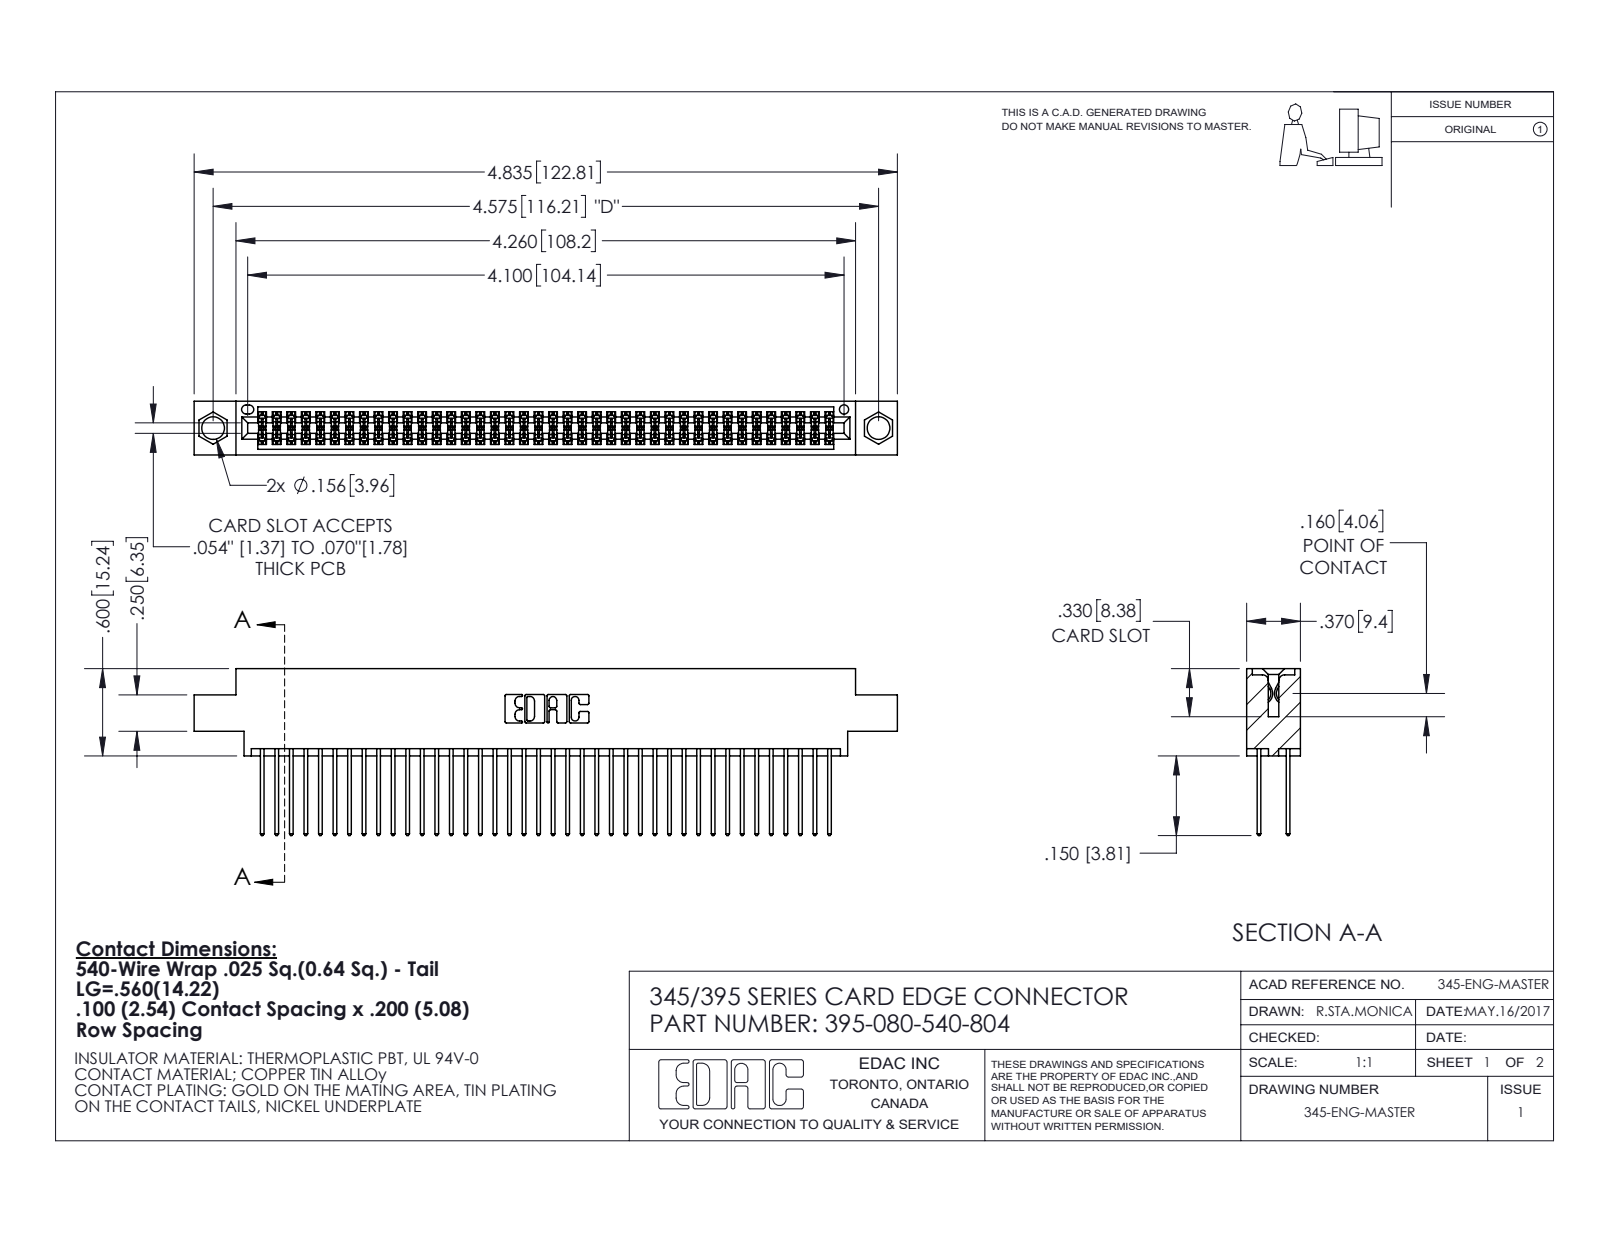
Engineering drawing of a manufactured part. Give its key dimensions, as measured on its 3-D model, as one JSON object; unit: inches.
{"part_name": "395-080-540-804; 345 Part_0.170 Offset - 0.156 Dia-TI; 345-292-001_345-293-140", "step_written_by": "SolidWorks 2020 (CONFIG_CONTROL_DESIGN)", "units": "inches", "bodies": {"solids": 81, "faces": 4144, "planar": 2738, "cylindrical": 1406, "other": 0}, "overall_size": [4.835, 1.147, 0.37], "volume_in3": 0.732, "surface_area_in2": 29.6, "round_holes": [[0.156, 2], [0.064, 1]], "partial_cylinders_radius": [[0.006, 120], [0.01, 80], [0.01, 22], [0.007, 6], [0.031, 6], [0.026, 3], [0.014, 2], [0.019, 2]], "face_to_face_distances": [0.072, 0.298, 0.2, 0.098, 0.272, 0.025, 0.37, 0.225, 0.175, 0.149], "hole_center_spacings": [0.27, 4.339, 4.575]}
